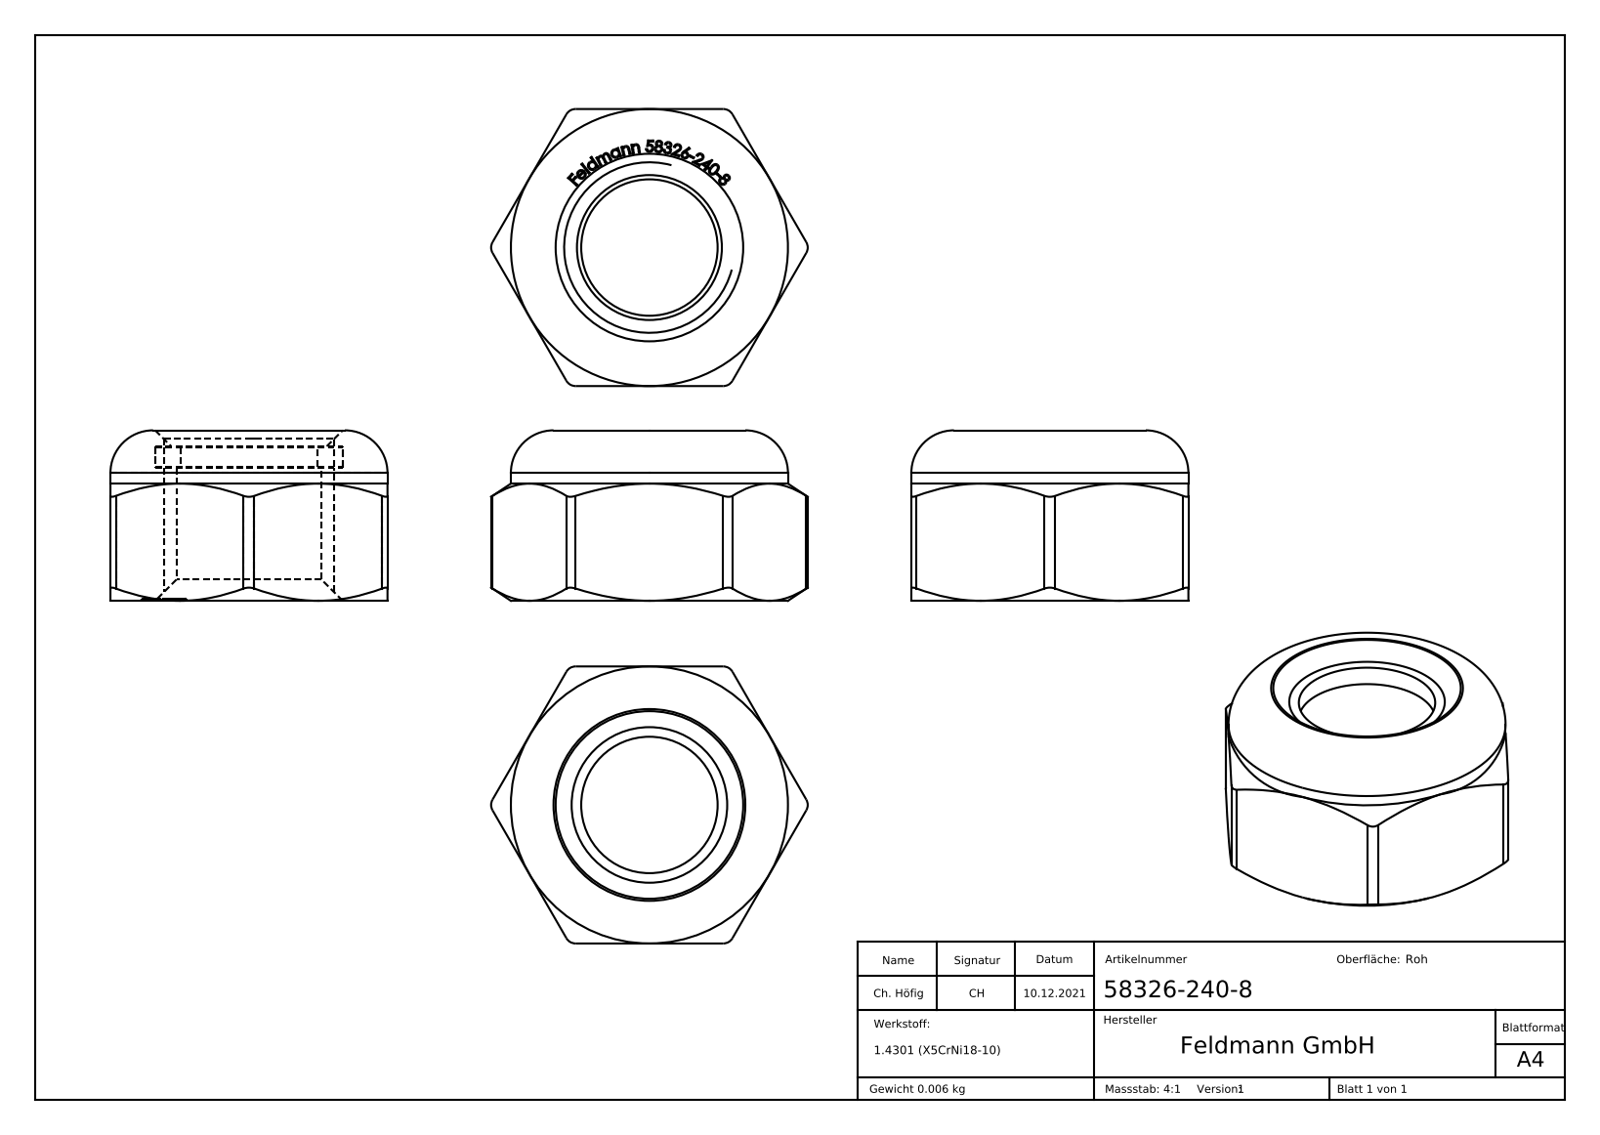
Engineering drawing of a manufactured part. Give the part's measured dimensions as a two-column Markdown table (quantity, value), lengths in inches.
| quantity | value |
| --- | --- |
| part name | 58326-240-8 |
| STEP written by | SolidWorks 2018 (CONFIG_CONTROL_DESIGN) |
| units | inches |
| bodies | 2 solids, 300 faces (140 planar, 11 cylindrical, 149 other) |
| overall size | 0.585 × 0.512 × 0.315 |
| volume | 0.048 in³ |
| surface area | 1.27 in² |
| round holes (diameter × count) | 0.252 × 1, 0.268 × 1, 0.346 × 1 |
| round bosses / shafts (diameter × count) | 0.512 × 1 |
| partial cylindrical surfaces (radius × count) | 0.02 × 6 |
| main face-to-face distances | 0.512, 0.037, 0.248, 0.283, 0.035, 0.246, 0.285, 0.039, 0.315, 0.069 |
